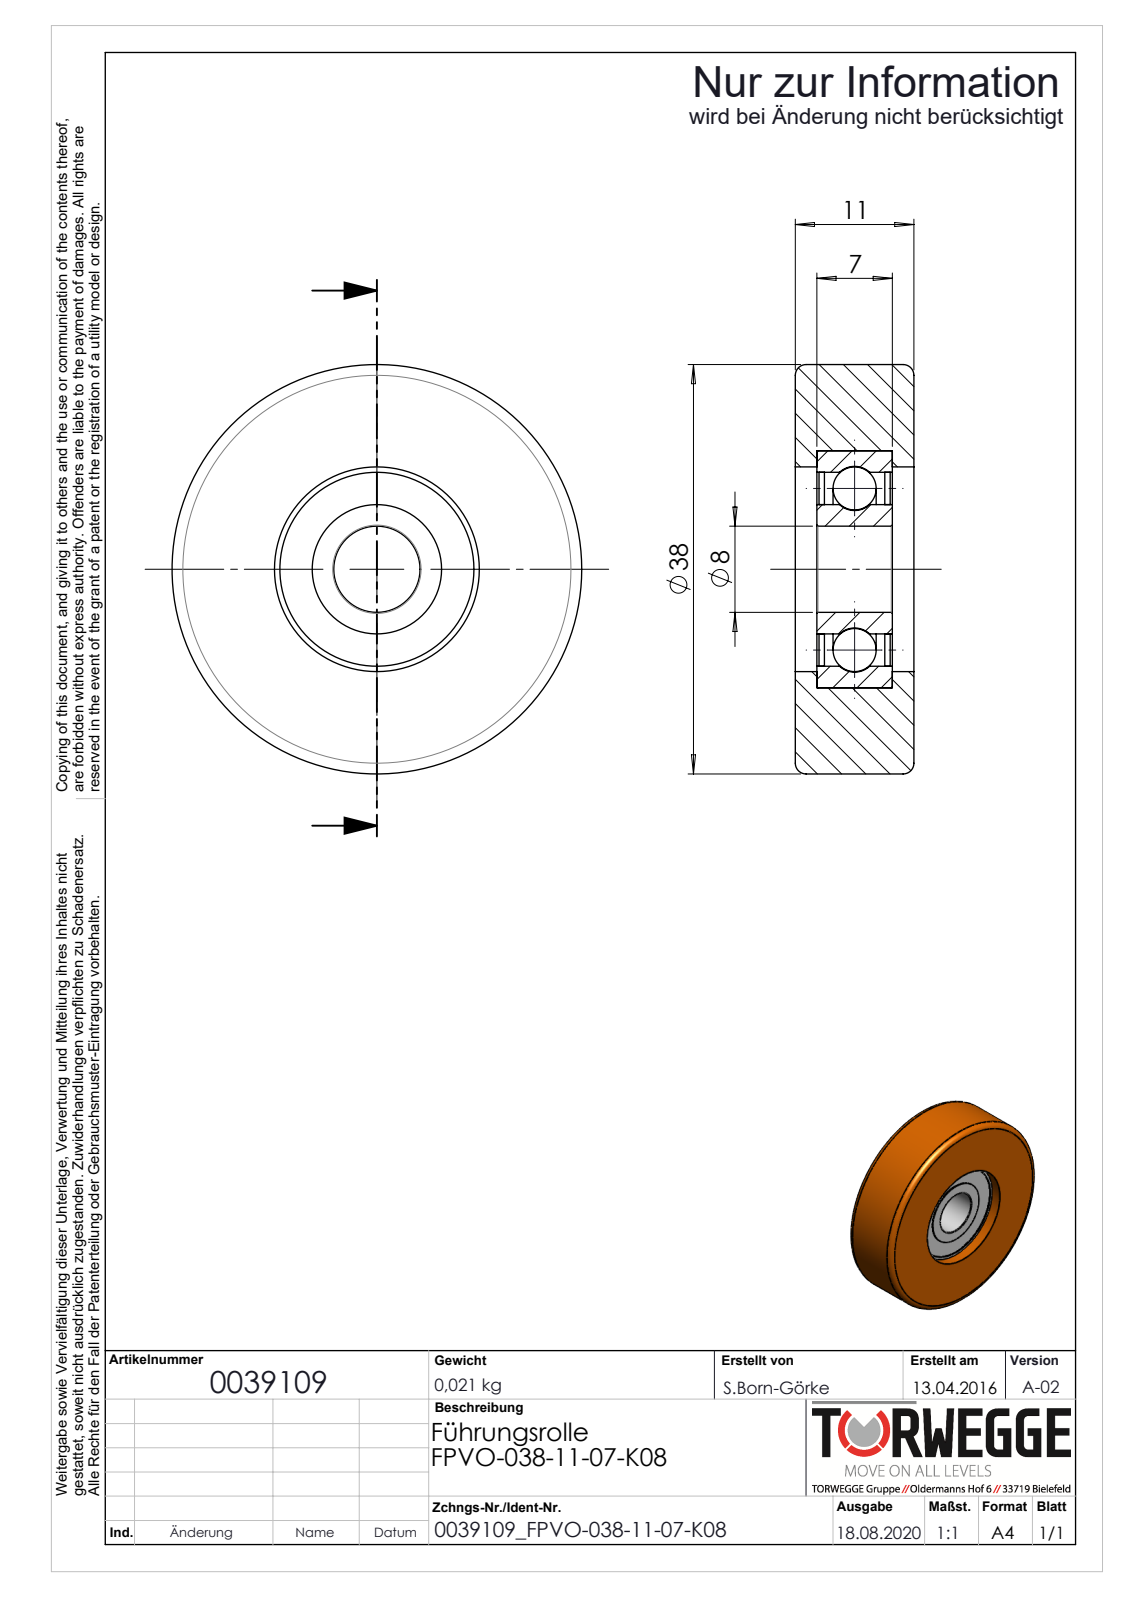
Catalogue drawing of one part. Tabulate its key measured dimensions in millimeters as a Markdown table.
| quantity | value |
| --- | --- |
| part name | 0039109 |
| STEP written by | SolidWorks 2018 (AUTOMOTIVE_DESIGN) |
| units | millimeters |
| bodies | 6 solids, 62 faces (12 planar, 28 cylindrical, 22 other) |
| overall size | 38 × 38 × 11 |
| volume | 10 583 mm³ |
| surface area | 6 793 mm² |
| round holes (diameter × count) | 8 × 1, 12 × 1, 18 × 1, 19 × 1, 22 × 1 |
| round bosses / shafts (diameter × count) | 38 × 1 |
| main face-to-face distances | 11, 2, 9, 2.2, 2.7, 8.3, 8.8, 0.7, 6.3, 6.8 |
